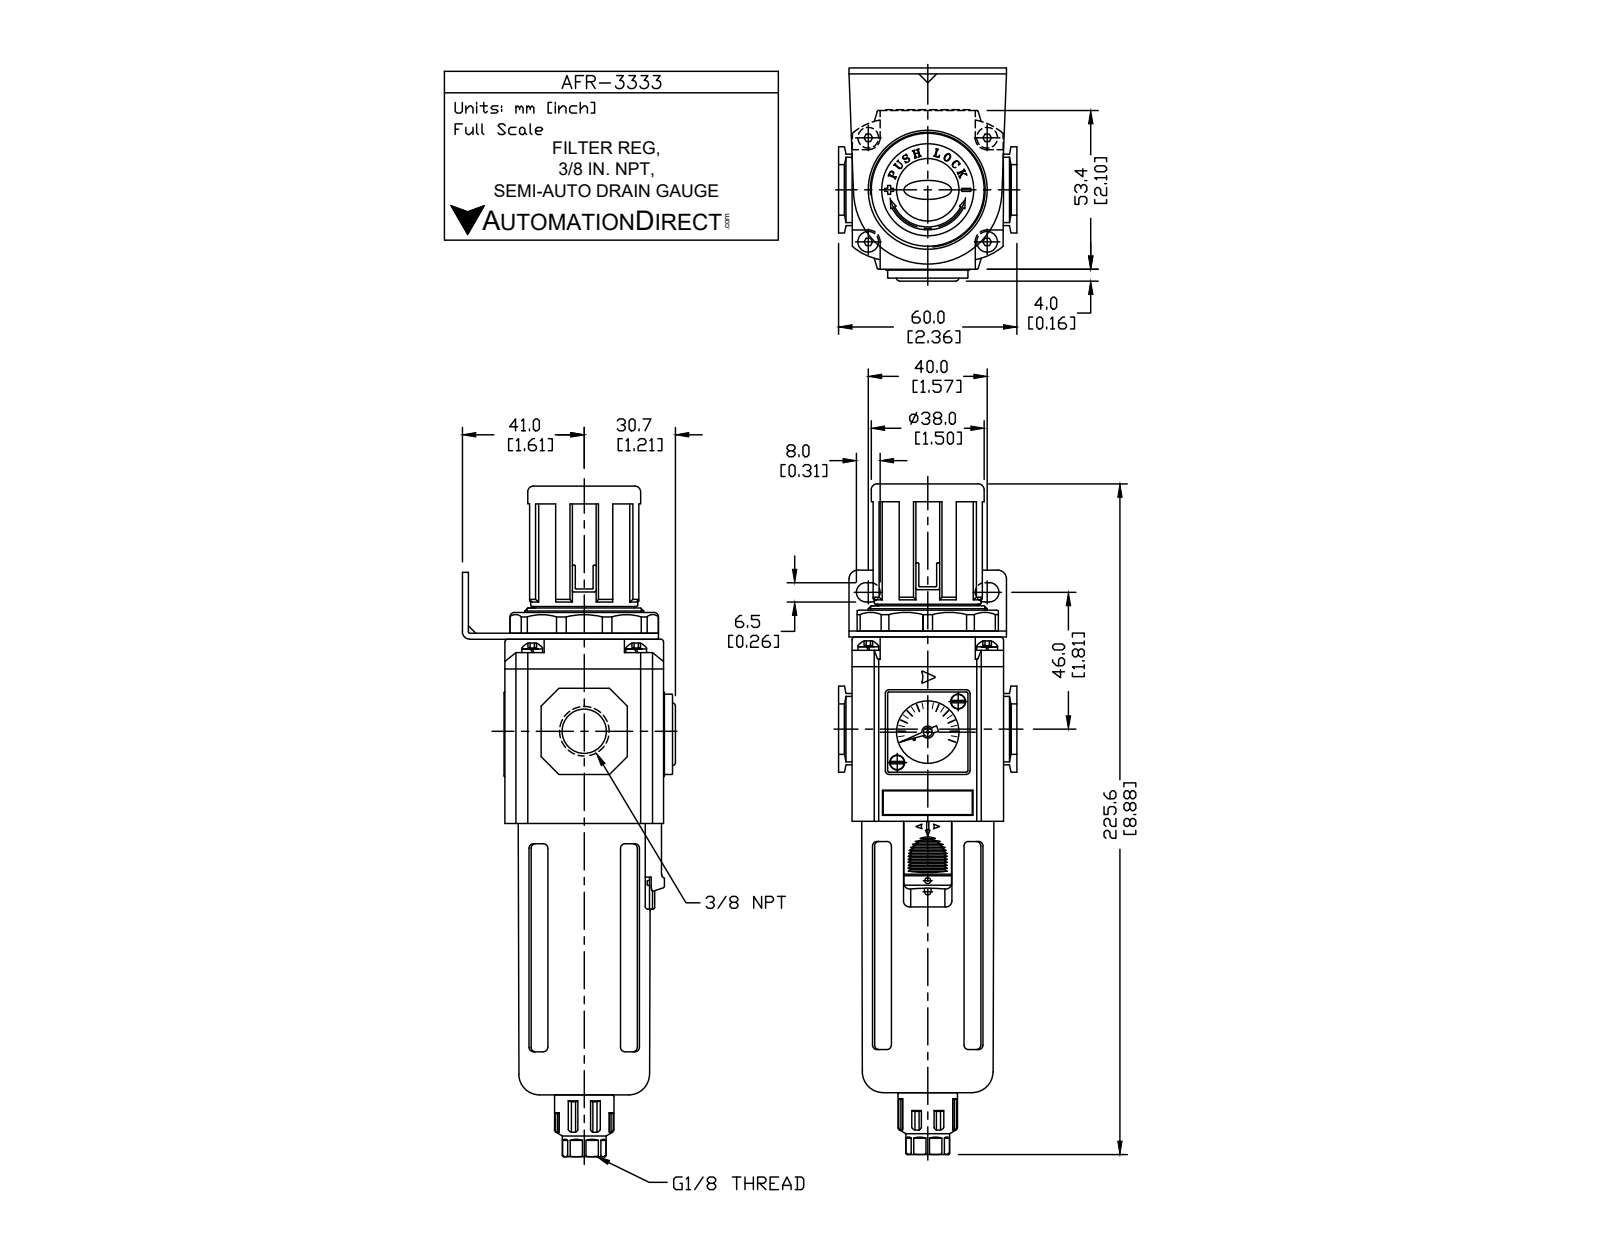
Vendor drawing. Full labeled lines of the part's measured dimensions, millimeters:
Part name (STEP PRODUCT): AFR-3333
STEP written by: SolidWorks 2015 (CONFIG_CONTROL_DESIGN)
Units: millimetres
Bodies: 16 solids, 606 faces (370 planar, 172 cylindrical, 64 other)
Overall size (bounding box): 225.6 × 72 × 60
Volume: 273 412 mm³ · Surface area: 70 223 mm²
Round holes (diameter × count): ⌀3 ×6, ⌀2 ×1, ⌀6.2 ×1, ⌀14.27 ×1, ⌀16 ×1, ⌀21 ×1, ⌀30 ×1, ⌀32 ×1, ⌀35.2 ×1
Round bosses / shafts (diameter × count): ⌀5.5 ×4, ⌀2.7 ×2, ⌀44 ×1, ⌀40 ×1, ⌀38 ×1, ⌀36 ×1, ⌀33.5 ×1, ⌀20.46 ×1
Partial cylindrical surfaces — rounded edges, fillets, slot ends (radius × count): R2.2 ×18, R1 ×12, R1.2 ×10, R0.5 ×8, R9.5 ×8, R3.25 ×6, R4 ×5, R0.3 ×4
Main face-to-face distances: 2, 62, 64, 53.4, 51, 39.6, 1, 55.5, 52.4, 4.5
Hole centre spacings: 26.58, 14.5, 35, 40, 53.15, 28.99
